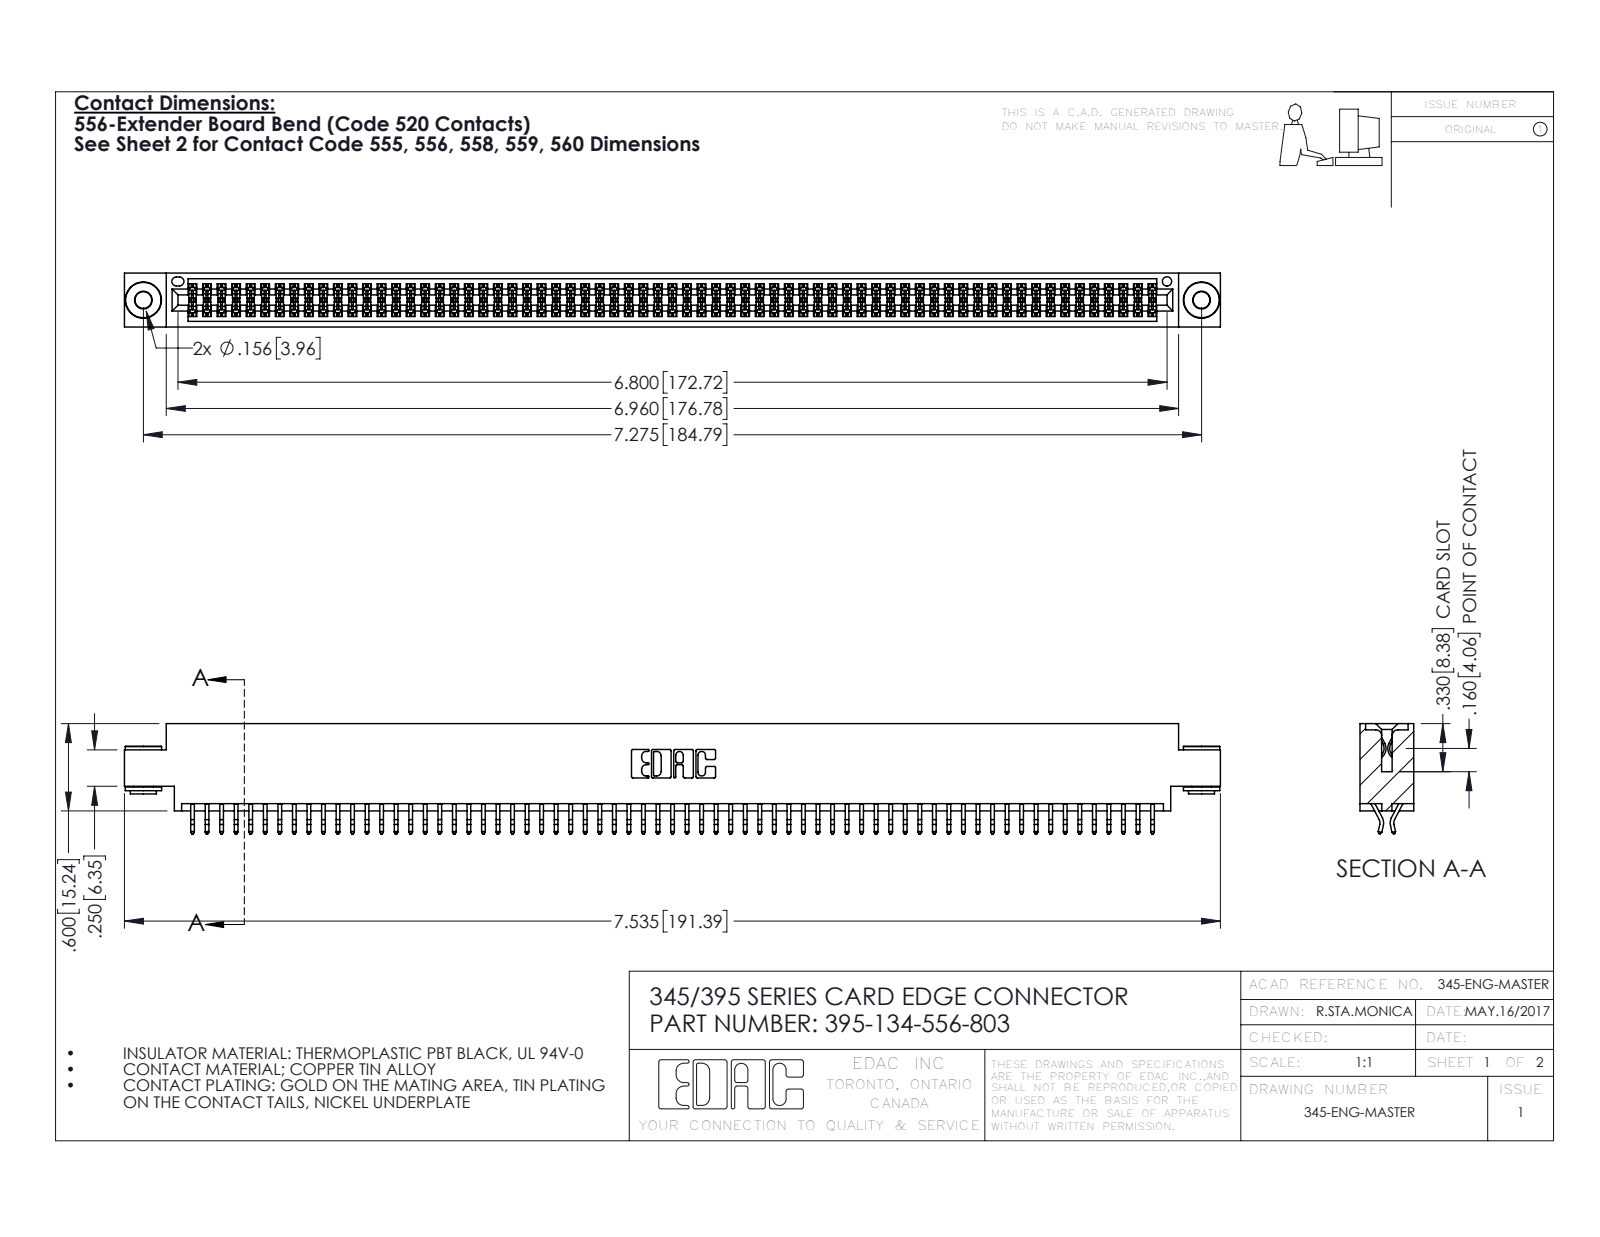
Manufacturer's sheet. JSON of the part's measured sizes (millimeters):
{"part_name": "345 Part_0.170 Offset - 0.156 Dia-TH; 345-250-002_345-250-002-102; 395-134-556-803; 345-292-001_556 Tail", "step_written_by": "SolidWorks 2016 (CONFIG_CONTROL_DESIGN)", "units": "millimeters", "bodies": {"solids": 137, "faces": 7672, "planar": 5052, "cylindrical": 2612, "other": 8}, "overall_size": [191.4, 19.2, 9.4], "volume_mm3": 18730, "surface_area_mm2": 28390, "round_holes": [[2.9, 2], [4, 2], [1.6, 1]], "round_bosses_or_shafts": [[6.4, 2], [4.6, 2], [3.5, 2]], "partial_cylinders_radius": [[0.2, 201], [0.3, 22], [0.2, 6], [0.8, 6], [0.7, 3], [0.3, 2], [0.4, 2], [0.5, 2]], "face_to_face_distances": [1.8, 7.6, 9.4, 5.1, 0.6, 2.5, 6.9, 5.7, 4.4, 3.8], "hole_center_spacings": [6.9, 178.8, 184.8]}
